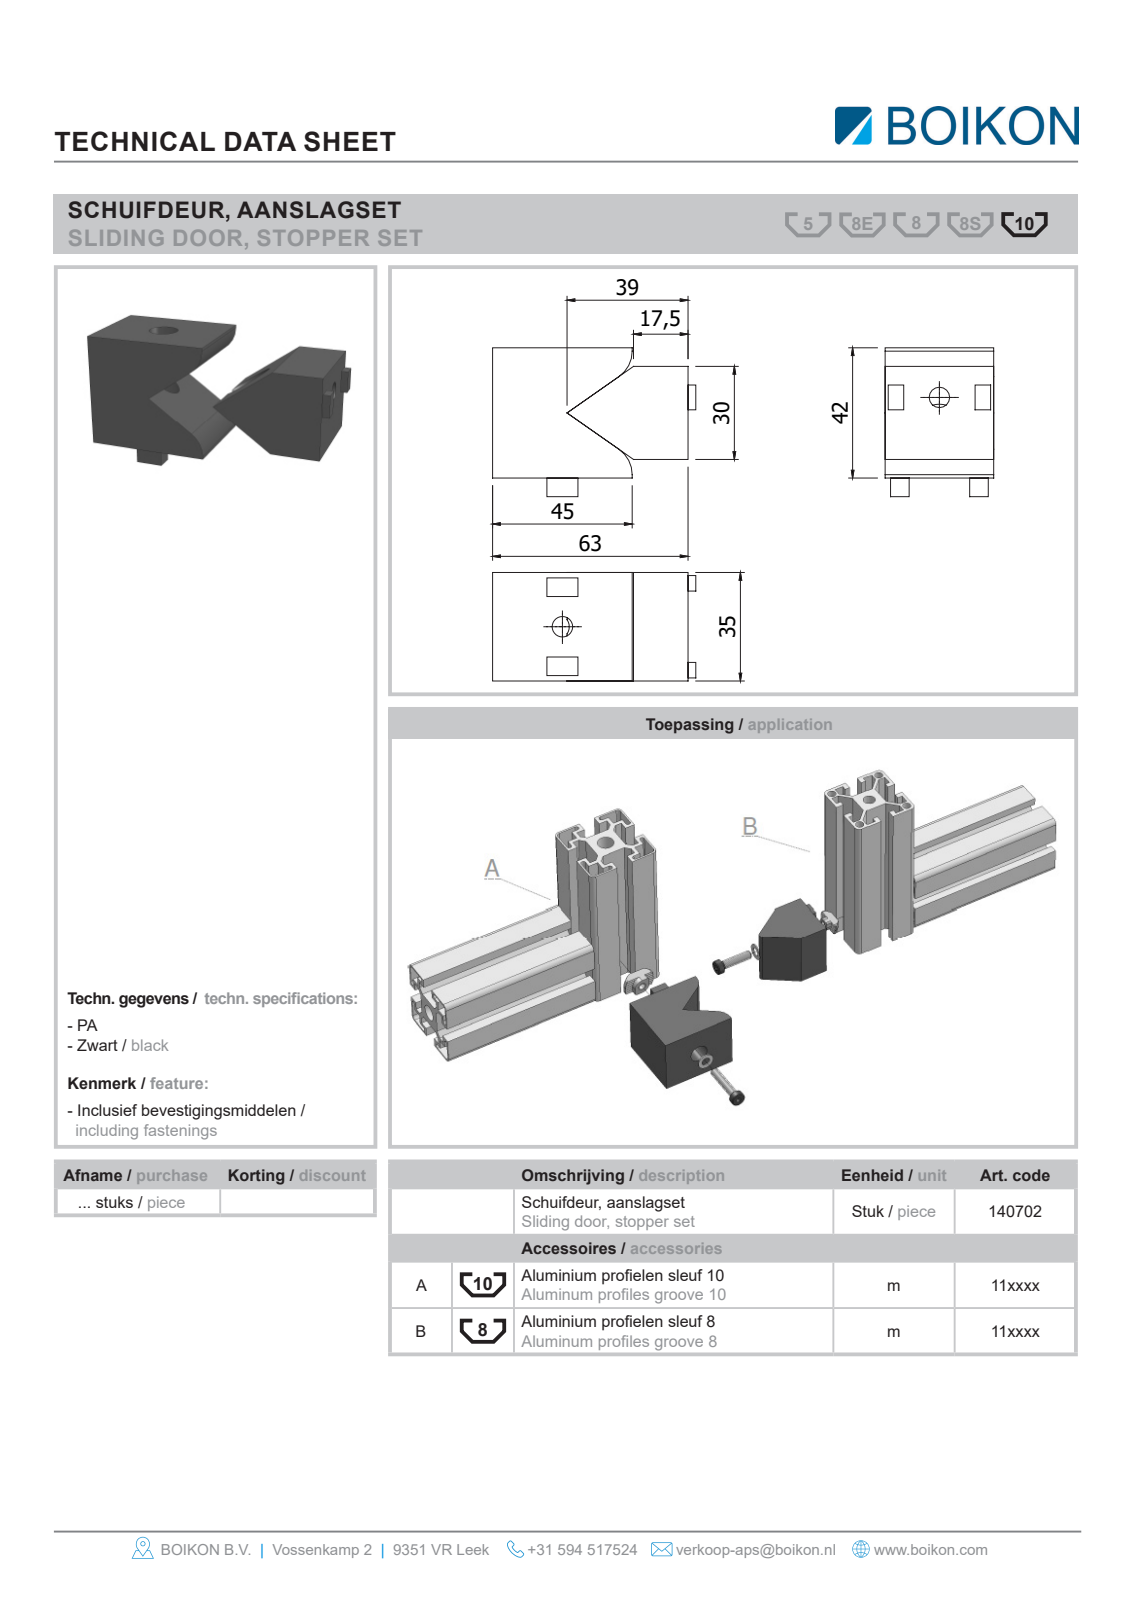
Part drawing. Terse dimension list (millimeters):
name: Root; 140702Schuifdeur aanslagsetBOIKON
written by: HiCAD 2013 1802.4 Build 509 (AUTOMOTIVE_DESIGN)
unit: mm
bodies: 2 solids, 44 faces (38 planar, 6 cylindrical, 0 other)
size: 65.5 × 48 × 35
volume: 80 287 mm³; area: 18 127 mm²
holes: 2× ⌀6.6, 2× ⌀11
rounds: 2× R10
face distances: 35, 42, 6, 36, 63, 30, 27.5, 48, 1.75, 27.25
